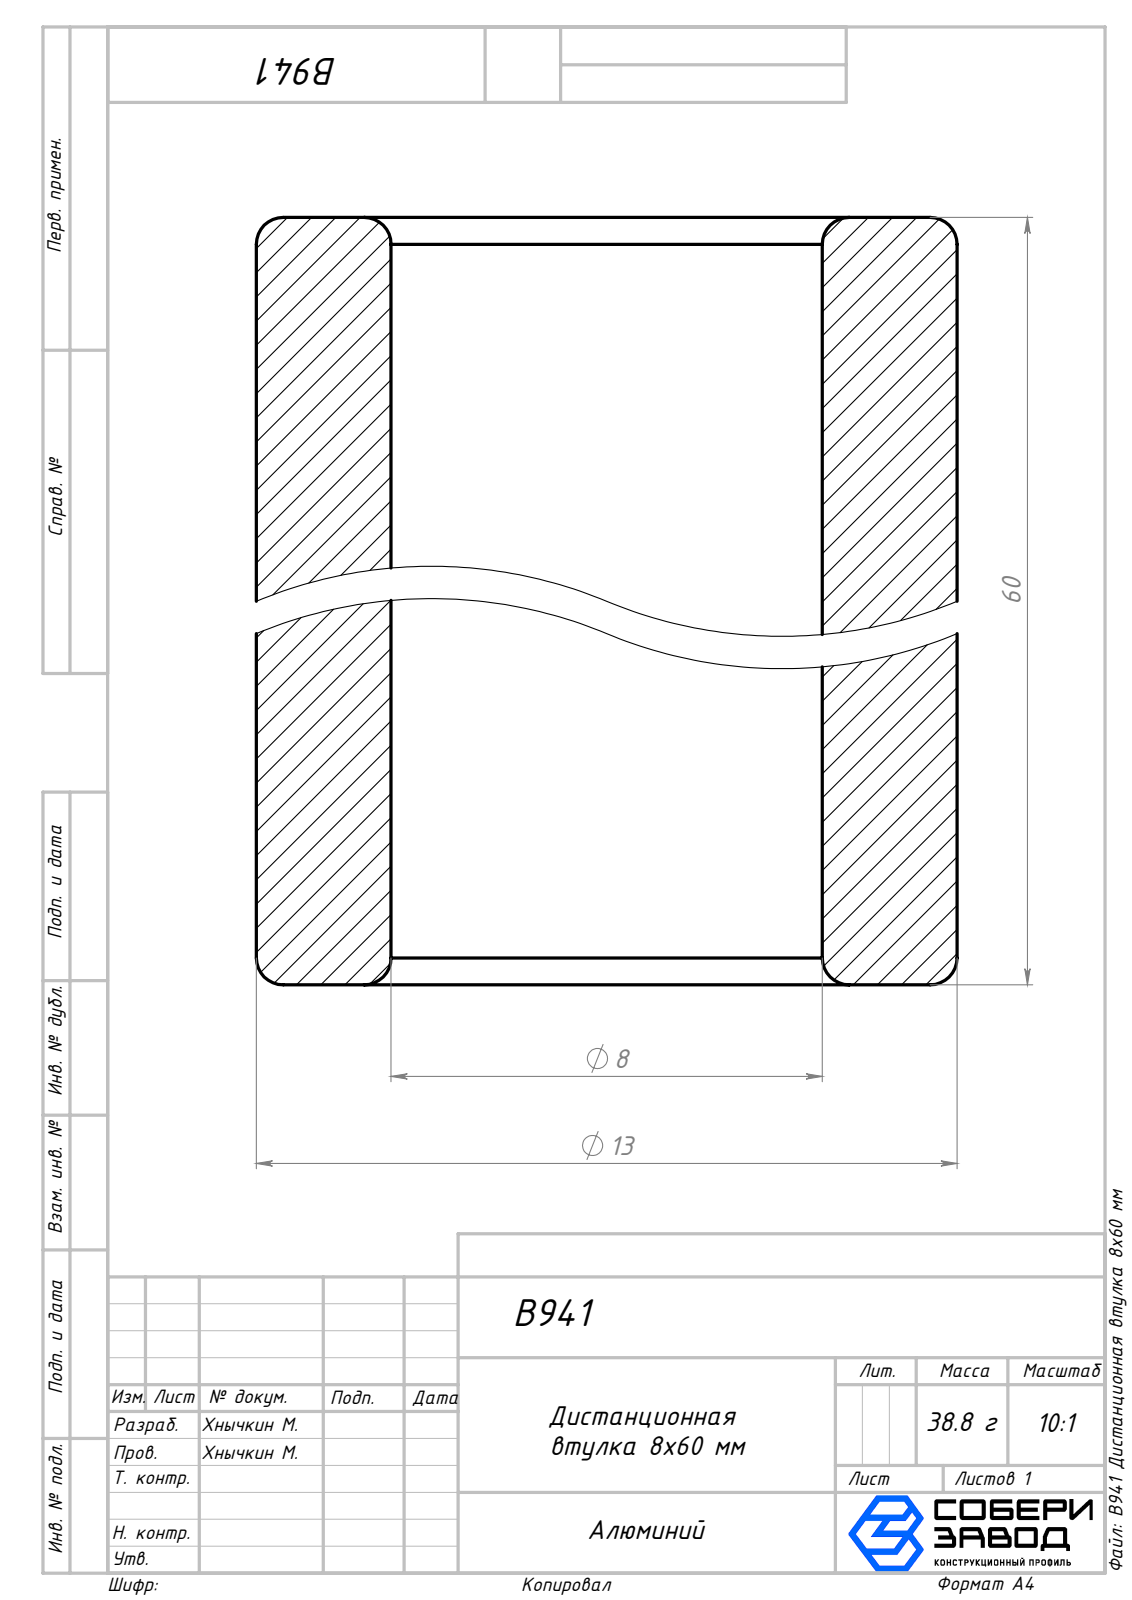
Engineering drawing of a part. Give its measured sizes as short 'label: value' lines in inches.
name: B941 Дистанционная втулка 8x60 мм
written by: SolidWorks 2026 (AUTOMOTIVE_DESIGN)
unit: in
bodies: 1 solid, 14 faces (2 planar, 4 cylindrical, 8 other)
size: 2.362 × 0.512 × 0.512
volume: 0.302 in³; area: 6.347 in²
holes: 1× ⌀0.315
bosses: 1× ⌀0.512
face distances: 2.362
